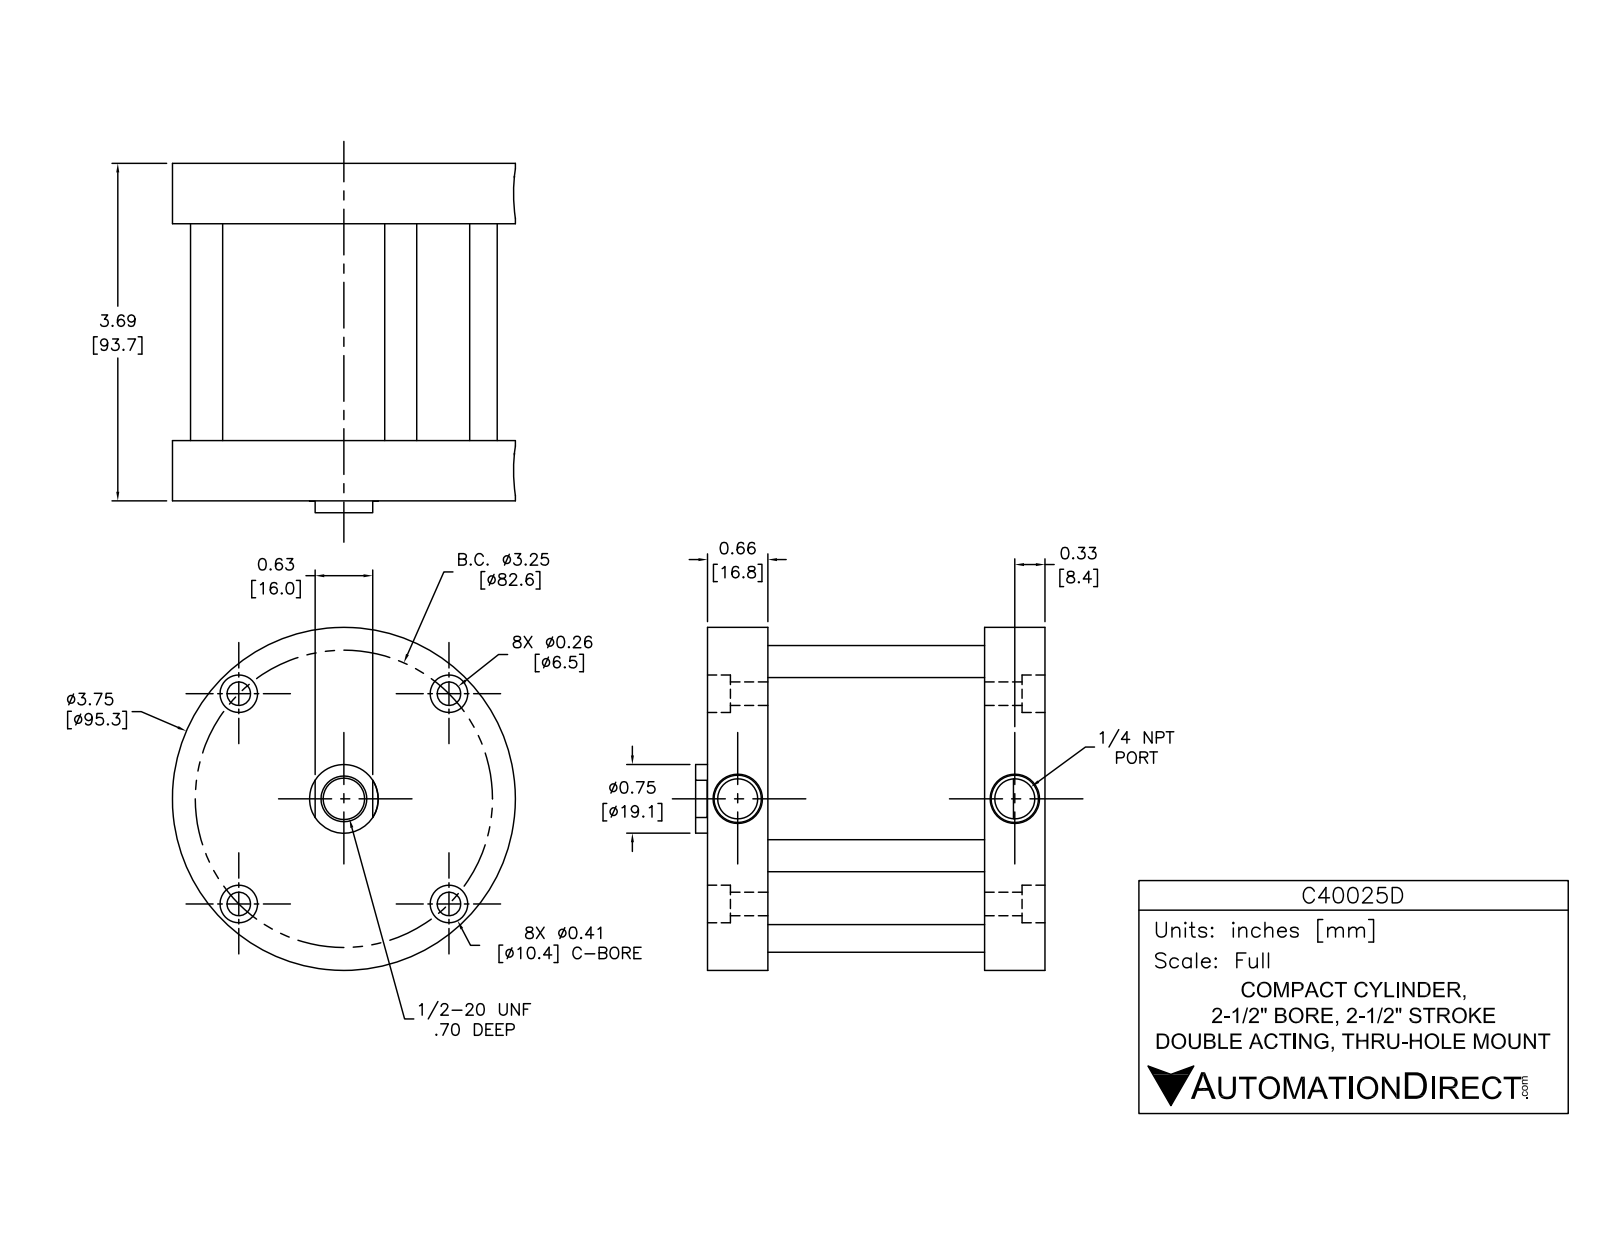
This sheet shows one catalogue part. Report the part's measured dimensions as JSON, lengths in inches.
{"part_name": "C40025D-FO1_BM_tube; C40025D-FO1_BM_heads; C40025D; C40025D-FO1_BM_r (+3 more)", "step_written_by": "SolidWorks 2014 (AUTOMOTIVE_DESIGN)", "units": "inches", "bodies": {"solids": 9, "faces": 165, "planar": 49, "cylindrical": 98, "other": 18}, "overall_size": [3.82, 3.75, 3.75], "volume_in3": 17.17, "surface_area_in2": 159.2, "round_holes": [[0.225, 4], [0.281, 4], [0.406, 4], [0.218, 2], [0.446, 1], [0.75, 1], [0.752, 1], [2.5, 1], [2.639, 1]], "round_bosses_or_shafts": [[0.45, 4], [0.225, 4], [3.75, 1]], "face_to_face_distances": [0.387, 3.303, 3.69, 2.916, 3.03, 2.643, 0.273, 0.66, 0.66, 0.273], "hole_center_spacings": [0.48, 1.625, 1.625, 1.933, 2.298, 2.298, 2.613, 3.215]}
